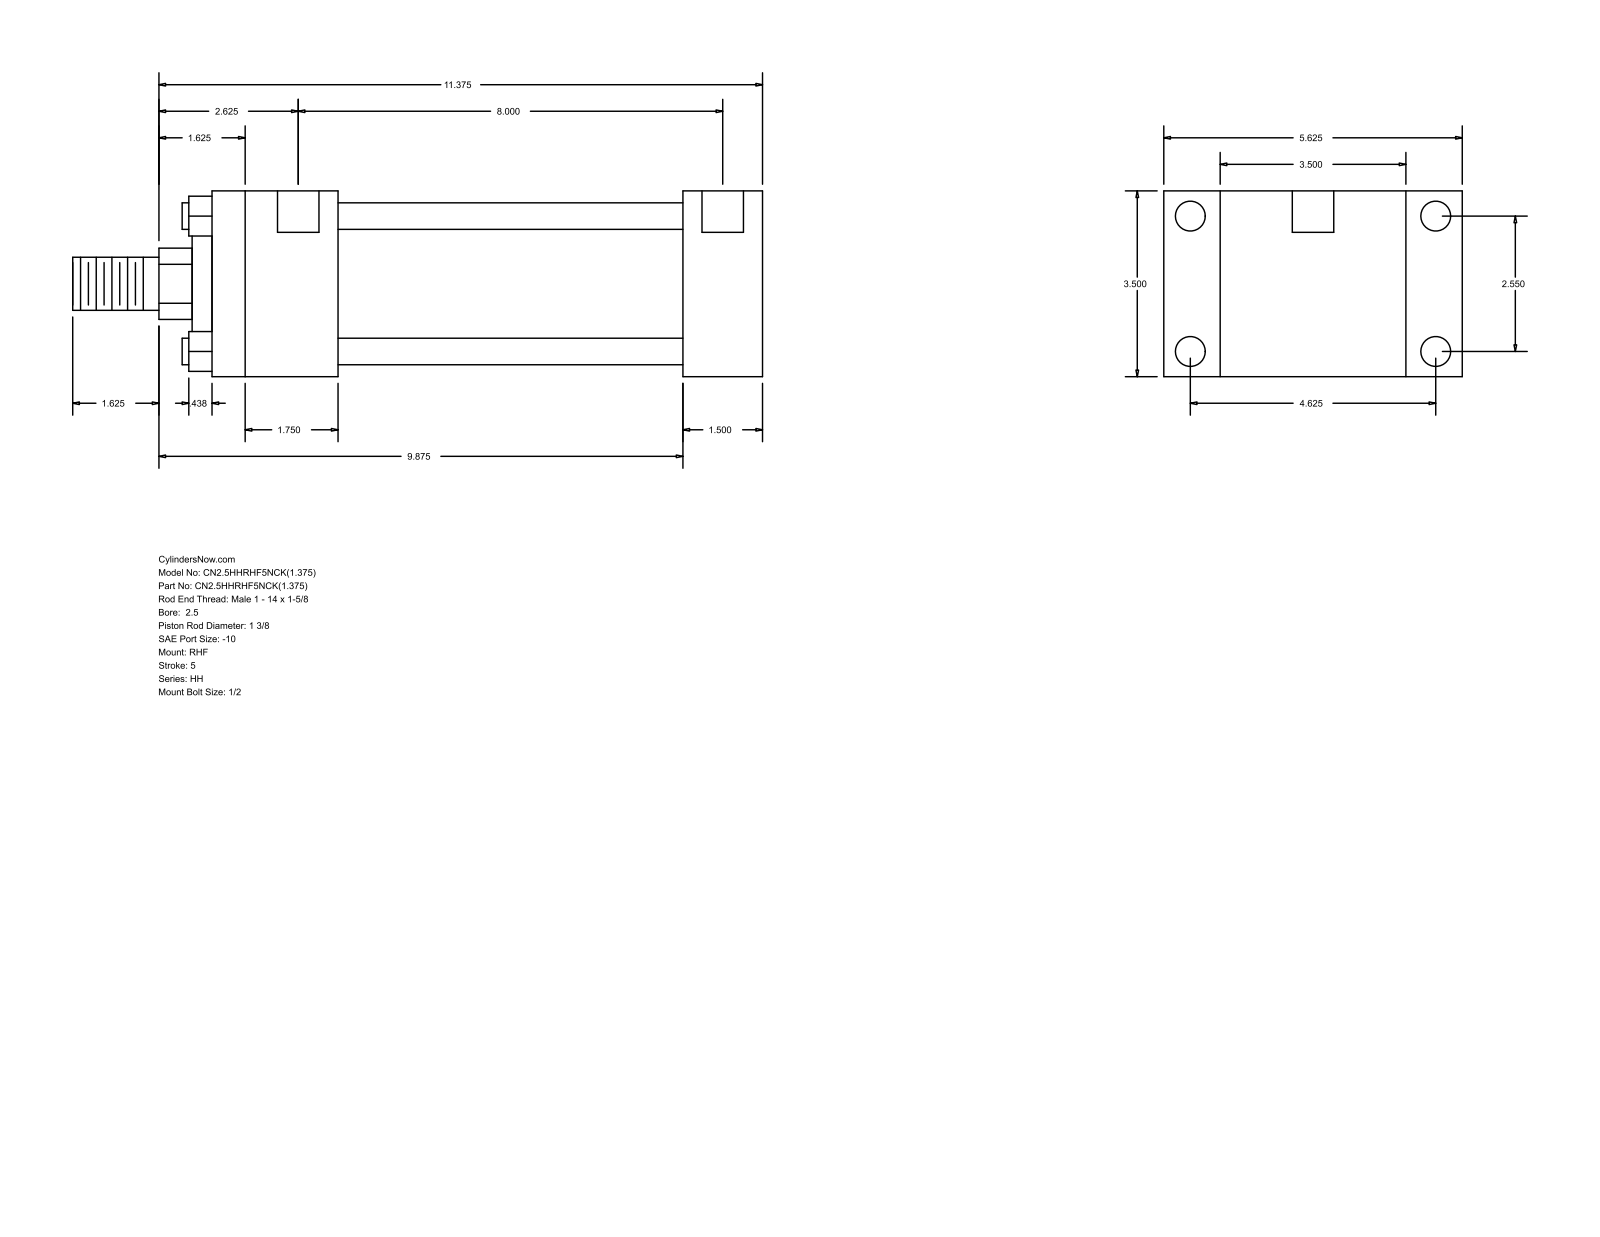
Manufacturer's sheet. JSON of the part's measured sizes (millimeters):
{"part_name": "HH_RHF__0250_1.375", "step_written_by": "GSSL Pune (CONFIG_CONTROL_DESIGN)", "units": "millimeters", "bodies": {"solids": 0, "faces": 88, "planar": 60, "cylindrical": 28, "other": 0}, "overall_size": [330.2, 142.88, 88.9], "round_holes": [[5.56, 4], [14.3, 4], [19.84, 2]], "round_bosses_or_shafts": [[12.7, 4], [73.03, 1], [50.8, 1], [34.92, 1], [25.4, 1]], "partial_cylinders_radius": [[17.06, 1]], "face_to_face_distances": [88.9, 38.11, 26.99, 115.89, 225.42, 263.53, 142.88, 60.32, 165.1, 203.21], "hole_center_spacings": [1.58, 64.76, 117.48, 134.15, 204.79, 206.37, 203.21]}
